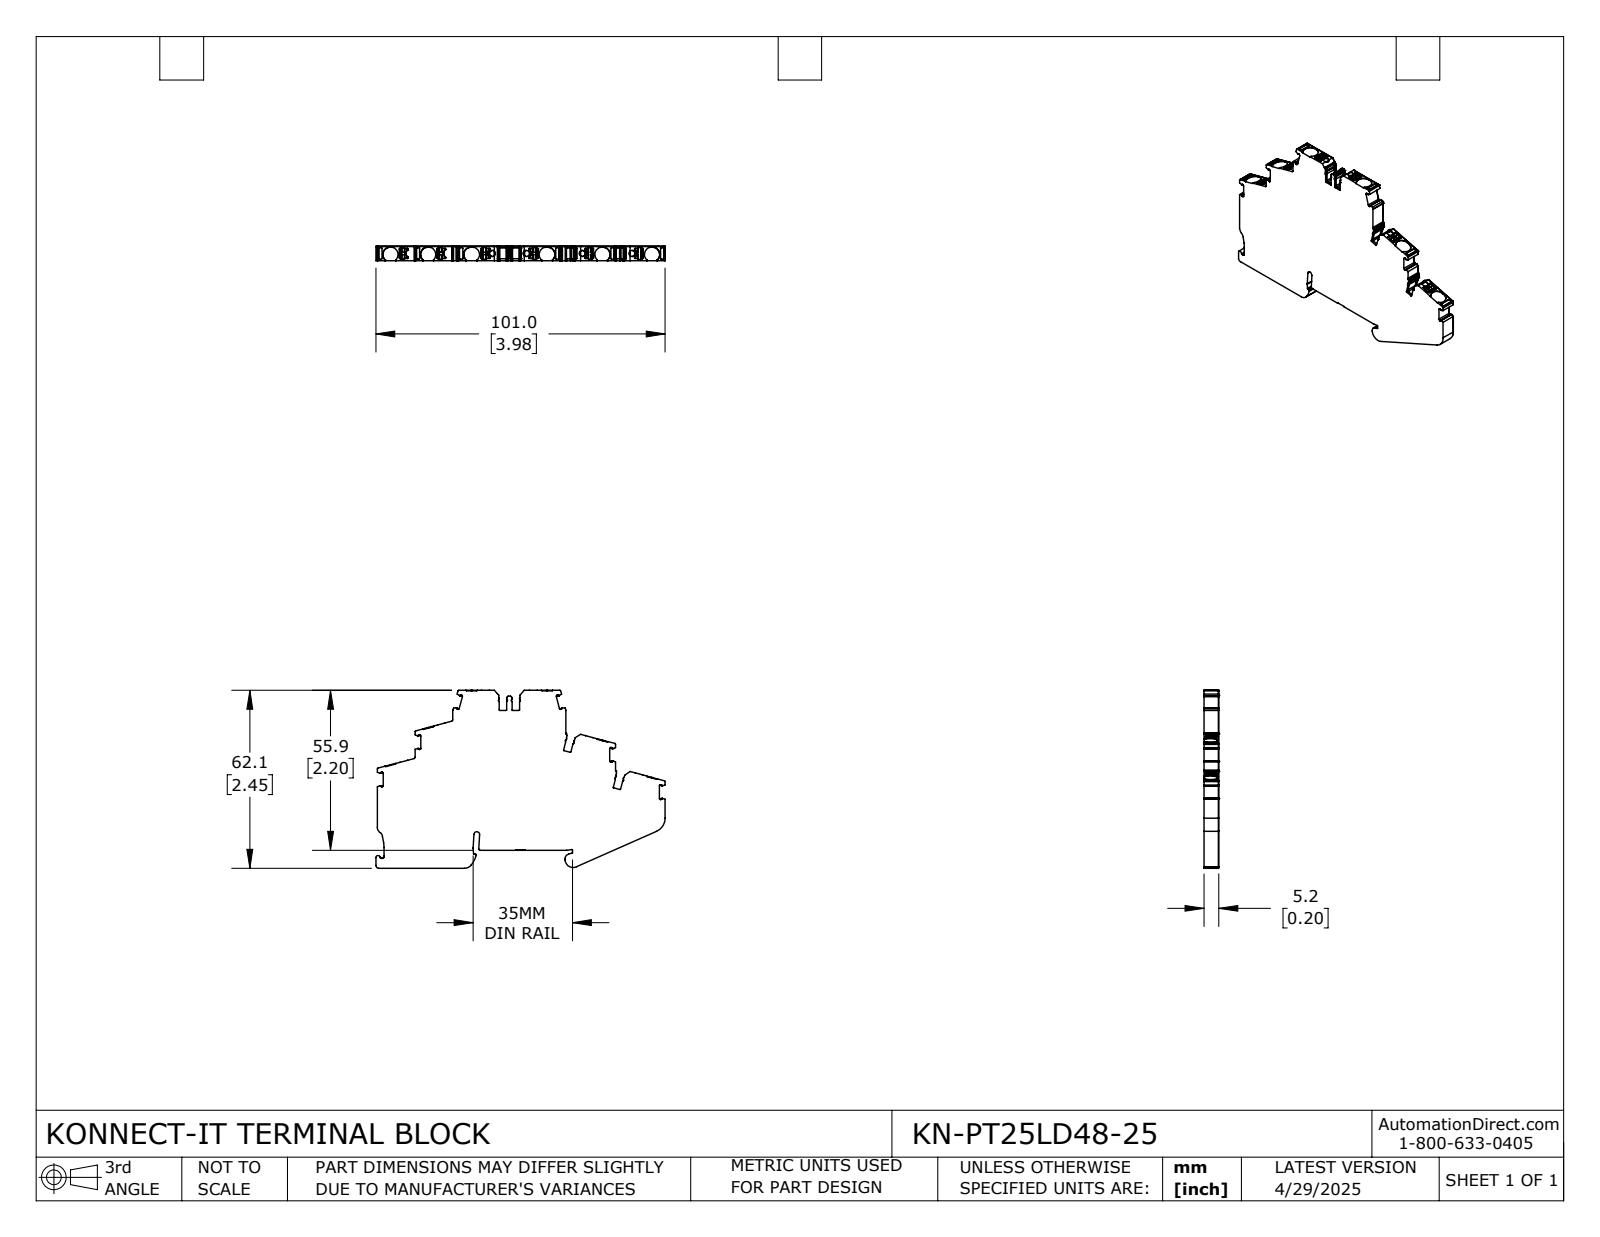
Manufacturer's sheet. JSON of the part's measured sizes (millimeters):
{"part_name": "KN-PT25LD48-25", "step_written_by": "SolidWorks 2024 (CONFIG_CONTROL_DESIGN)", "units": "millimeters", "bodies": {"solids": 1, "faces": 1212, "planar": 579, "cylindrical": 528, "other": 105}, "overall_size": [101, 62.1, 5.2], "volume_mm3": 22190, "surface_area_mm2": 10810, "round_holes": [[2.1, 4]], "partial_cylinders_radius": [[0.2, 128], [0.1, 49], [0.3, 47], [0.5, 26], [0.2, 24], [0.4, 17], [0.6, 14], [0.2, 12]], "face_to_face_distances": [5.2, 6.2, 2, 55.7, 61.9, 8.1, 17.3, 13.2, 62.1, 55.9], "hole_center_spacings": [11.8, 20.1]}
